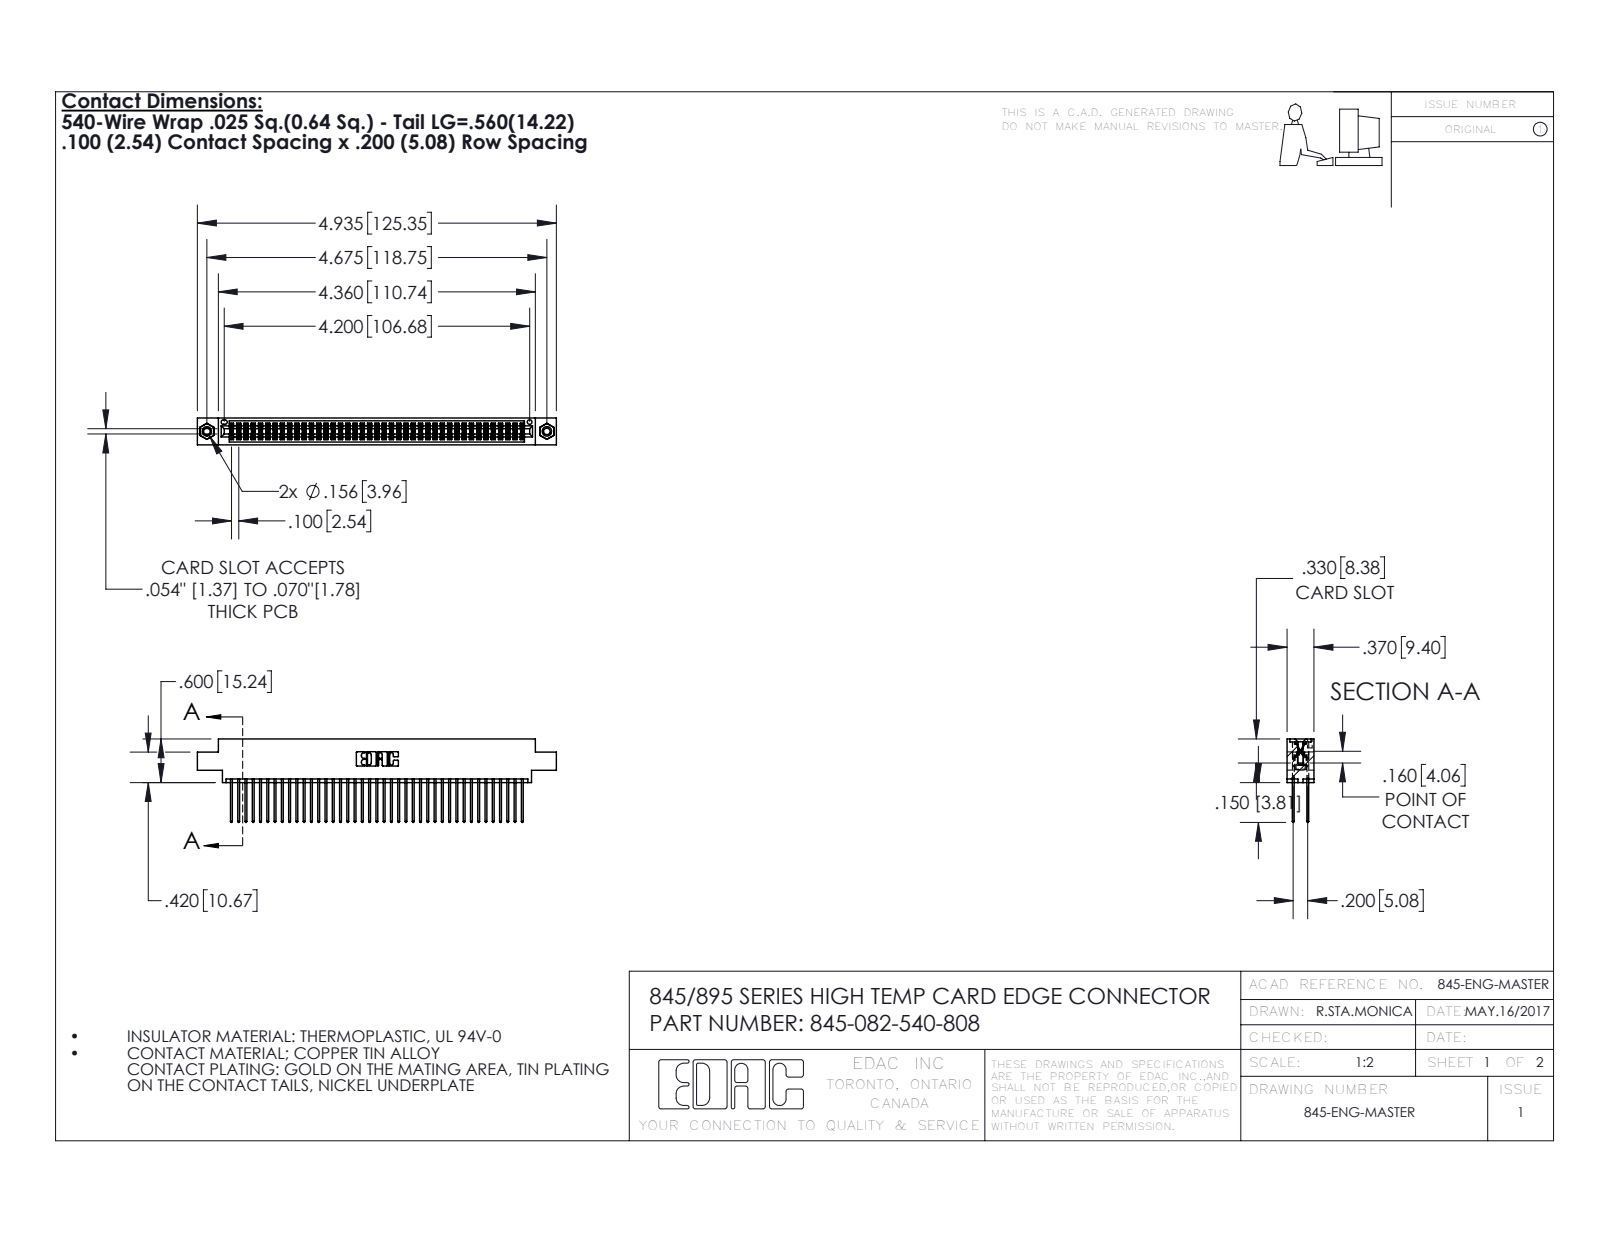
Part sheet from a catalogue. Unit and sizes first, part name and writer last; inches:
Units: inches
Overall size (bounding box): 4.935 × 1.147 × 0.37
Round holes (diameter × count): ⌀0.089 ×2, ⌀0.125 ×2, ⌀0.156 ×2, ⌀0.064 ×1
Round bosses / shafts (diameter × count): ⌀0.155 ×2
Partial cylindrical surfaces — rounded edges, fillets, slot ends (radius × count): R0.006 ×123, R0.01 ×82, R0.01 ×22, R0.007 ×6, R0.031 ×6, R0.026 ×3, R0.014 ×2, R0.019 ×2
Main face-to-face distances: 0.072, 0.298, 0.2, 0.098, 0.272, 0.025, 0.37, 0.225, 0.175, 0.149
Hole centre spacings: 0.27, 4.439, 4.675
Volume: 0.754 in³ · Surface area: 30.76 in²
Bodies: 85 solids, 4290 faces (2822 planar, 1452 cylindrical, 16 other)
Part name (STEP PRODUCT): 345-250-001_345-250-003-102; 345 Part_0.170 Offset - 0.156 Dia-TI; 345-292-001_345-293-140; 345-082-540-808
STEP written by: SolidWorks 2016 (CONFIG_CONTROL_DESIGN)
